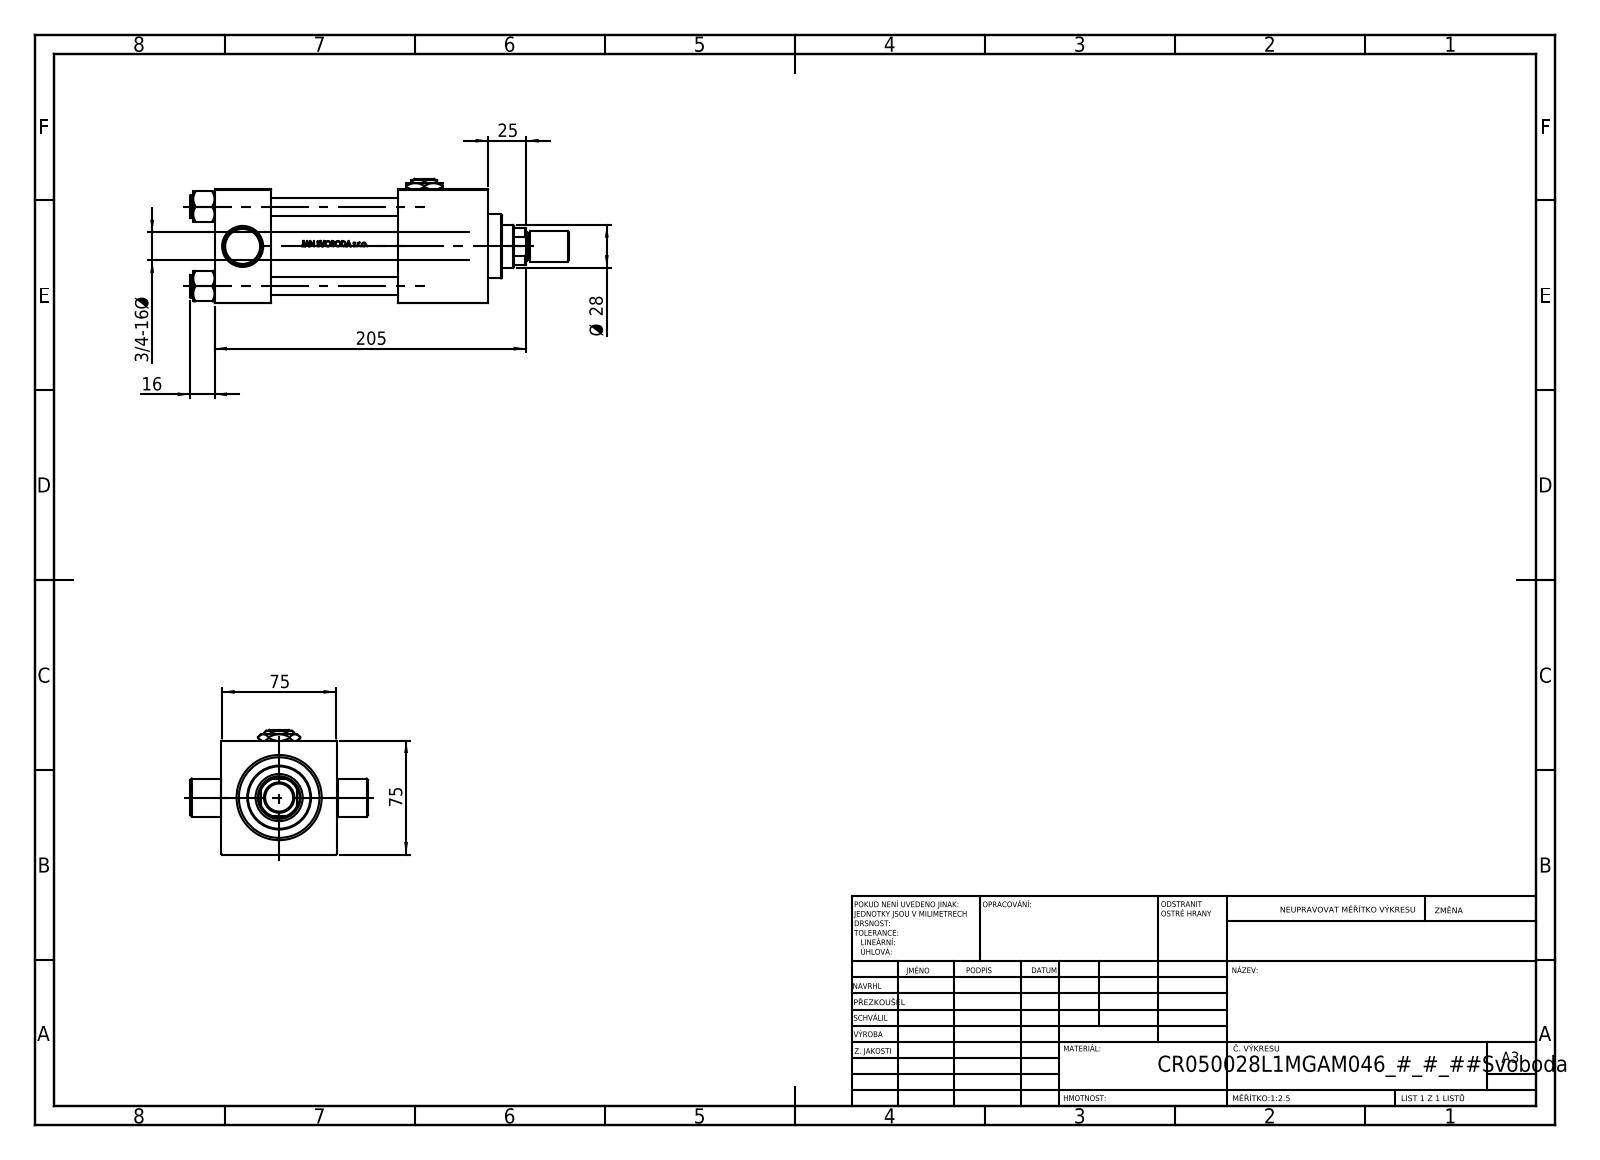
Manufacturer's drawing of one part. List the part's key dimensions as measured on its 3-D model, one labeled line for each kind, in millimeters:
Part name (STEP PRODUCT): NUT_M5_L; ROD_END_AH; V215CR_VCP_L; V215CR_L_Body (+3 more)
STEP written by: SolidWorks 2019 (CONFIG_CONTROL_DESIGN)
Units: millimetres
Bodies: 13 solids, 1133 faces (455 planar, 128 cylindrical, 550 other)
Overall size (bounding box): 249 × 117 × 82
Volume: 748 381 mm³ · Surface area: 168 485 mm²
Round holes (diameter × count): ⌀12 ×4, ⌀7 ×2, ⌀20.96 ×2, ⌀30 ×2, ⌀18.5 ×1, ⌀28 ×1, ⌀31 ×1, ⌀41 ×1, ⌀50 ×1, ⌀53 ×1
Round bosses / shafts (diameter × count): ⌀15 ×4, ⌀56 ×1, ⌀42 ×1, ⌀25 ×1, ⌀20 ×1, ⌀18 ×1
Partial cylindrical surfaces — rounded edges, fillets, slot ends (radius × count): R13.5 ×1
Main face-to-face distances: 75, 37, 0.5, 76, 75.5, 59, 180, 143, 84, 121
Hole centre spacings: 36.98, 52.3, 73.96, 119.5
